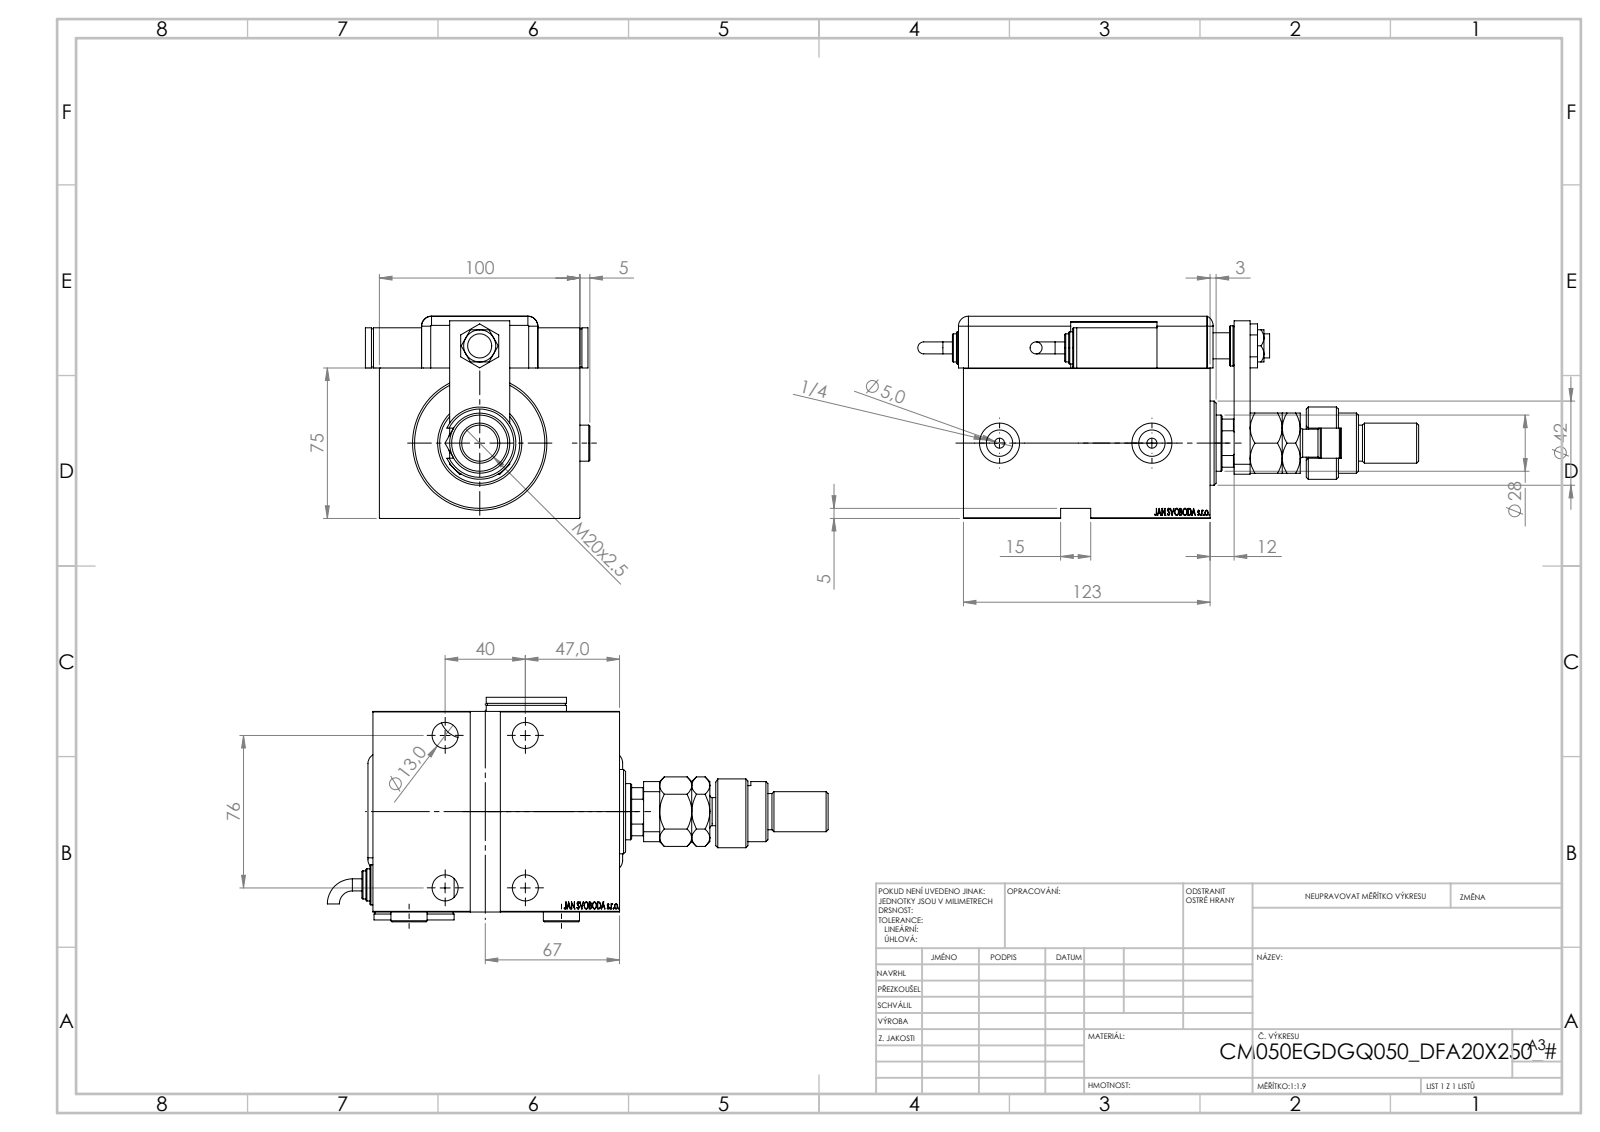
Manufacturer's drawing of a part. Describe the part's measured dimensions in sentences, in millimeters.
The part is named "V450CM_E_Body; KRYT; SWITCH DIM A_G; TYC (+7 more)". Its 3-D file was written by "SolidWorks 2019 (CONFIG_CONTROL_DESIGN)". It is 17 solids with 1381 faces: 680 planar, 136 cylindrical and 565 other. Overall it measures 249.76 by 111.9 by 100.8 millimeters. Its volume is 1 001 000 cubic millimeters and its surface area 196 760 square millimeters. Round holes: 5 of diameter 13, 4 of diameter 19, 3 of diameter 20, 2 of diameter 4, 2 of diameter 5, 2 of diameter 8, 2 of diameter 13.16, 1 of diameter 12, 1 of diameter 14, 1 of diameter 18.5, 1 of diameter 28, 1 of diameter 31.5. Round bosses or shafts: 3 of diameter 20, 3 of diameter 18, 3 of diameter 14, 2 of diameter 16, 2 of diameter 6, 1 of diameter 52, 1 of diameter 42, 1 of diameter 36. Partial cylindrical surfaces (rounded edges, fillets, slot ends): 9 of radius 5, 1 of radius 7.5, 1 of radius 10, 1 of radius 12, 1 of radius 13.5. The main face-to-face distances are 3, 75, 100, 123, 100.8, 25.8, 20, 14, 109, 25. The hole center spacings are 76, 40, 47.2, 61.22, 82.87, 85.88, 91.59, 20.
